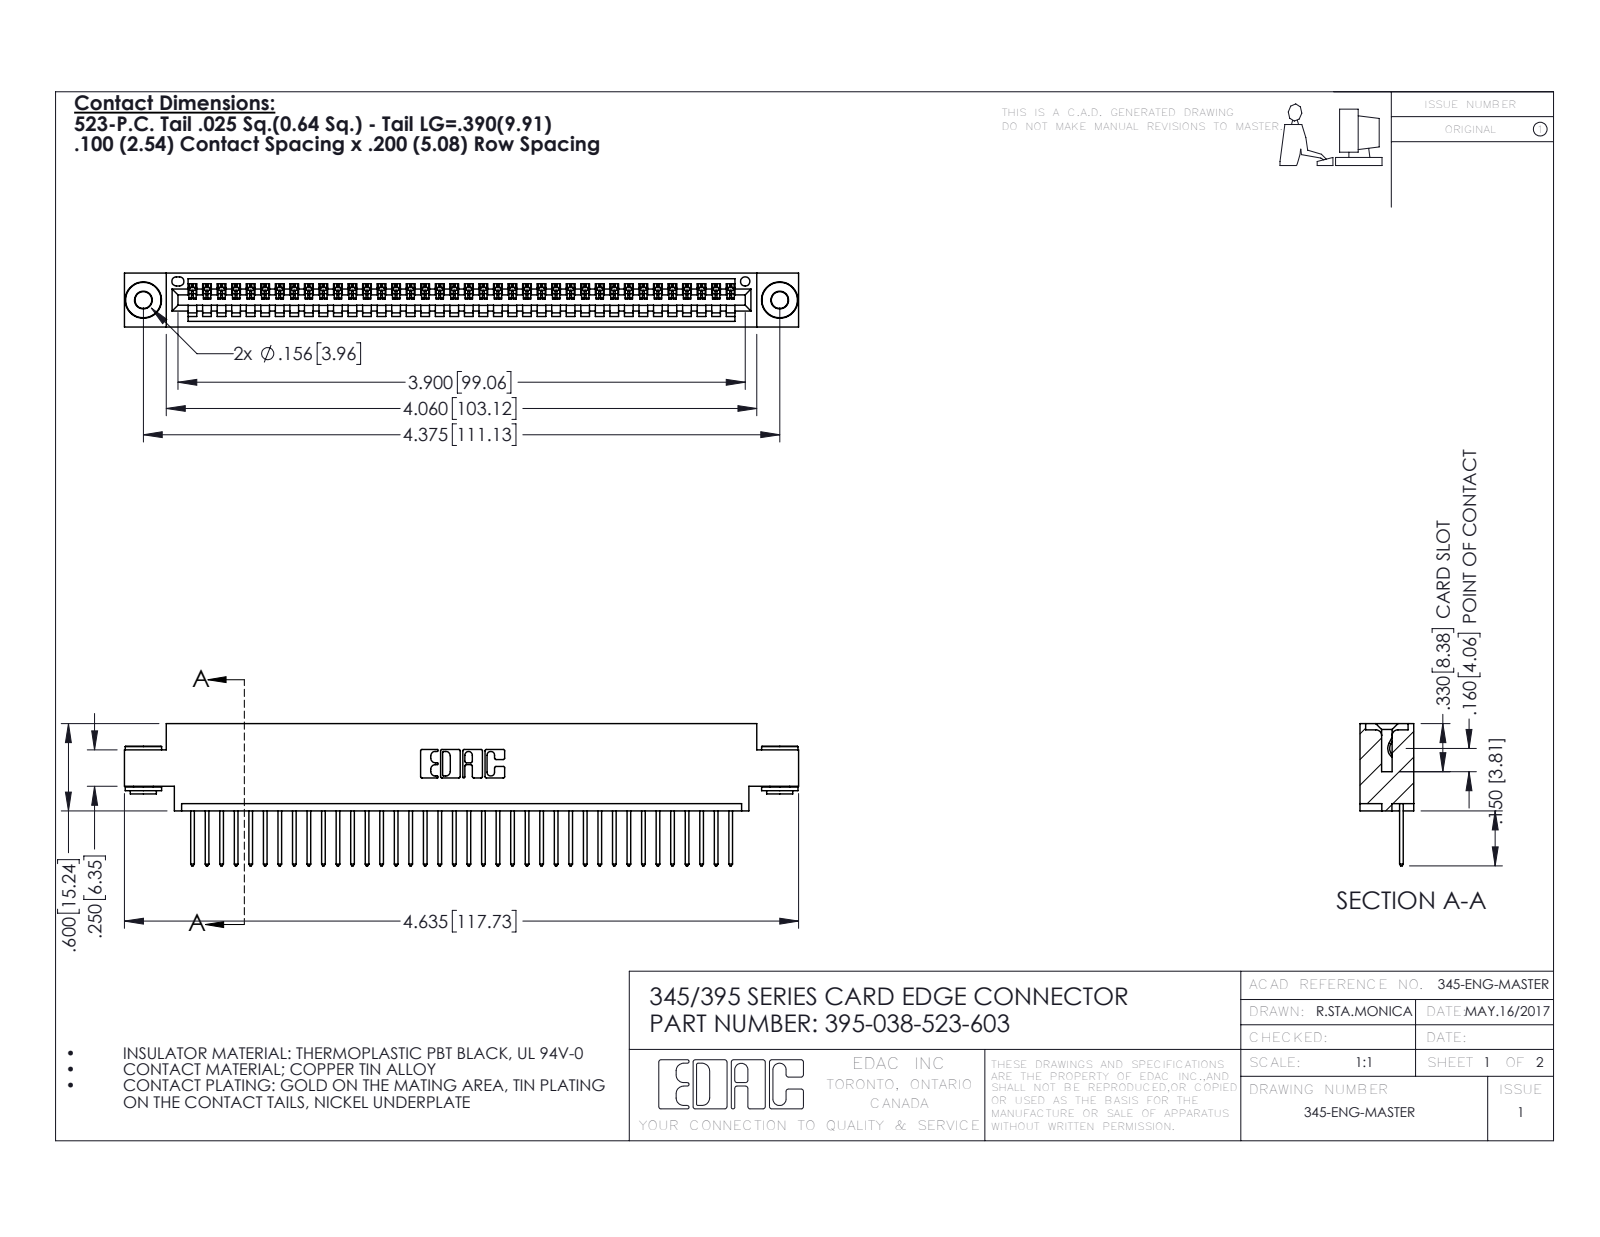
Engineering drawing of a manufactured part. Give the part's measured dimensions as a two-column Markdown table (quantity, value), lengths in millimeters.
| quantity | value |
| --- | --- |
| part name | 345-250-002_345-250-002-102; 345 Part_0.170 Offset - 0.156 Dia-TH; 395-038-523-603; 345-292-001_345-293-123 |
| STEP written by | SolidWorks 2016 (CONFIG_CONTROL_DESIGN) |
| units | millimeters |
| bodies | 41 solids, 2372 faces (1614 planar, 750 cylindrical, 8 other) |
| overall size | 117.7 × 24.8 × 9.4 |
| volume | 11 000 mm³ |
| surface area | 15 000 mm² |
| round holes (diameter × count) | 2.9 × 2, 4 × 2, 1.6 × 1 |
| round bosses / shafts (diameter × count) | 6.4 × 2, 4.6 × 2, 3.5 × 2 |
| partial cylindrical surfaces (radius × count) | 0.2 × 76, 0.3 × 76, 0.3 × 22, 0.2 × 6, 0.8 × 6, 0.7 × 3, 0.8 × 2, 1 × 2 |
| main face-to-face distances | 1.8, 7.6, 9.4, 5.1, 2.5, 6.9, 0.6, 5.7, 4.4, 3.8 |
| hole center spacings | 6.9, 105.1, 111.1 |
